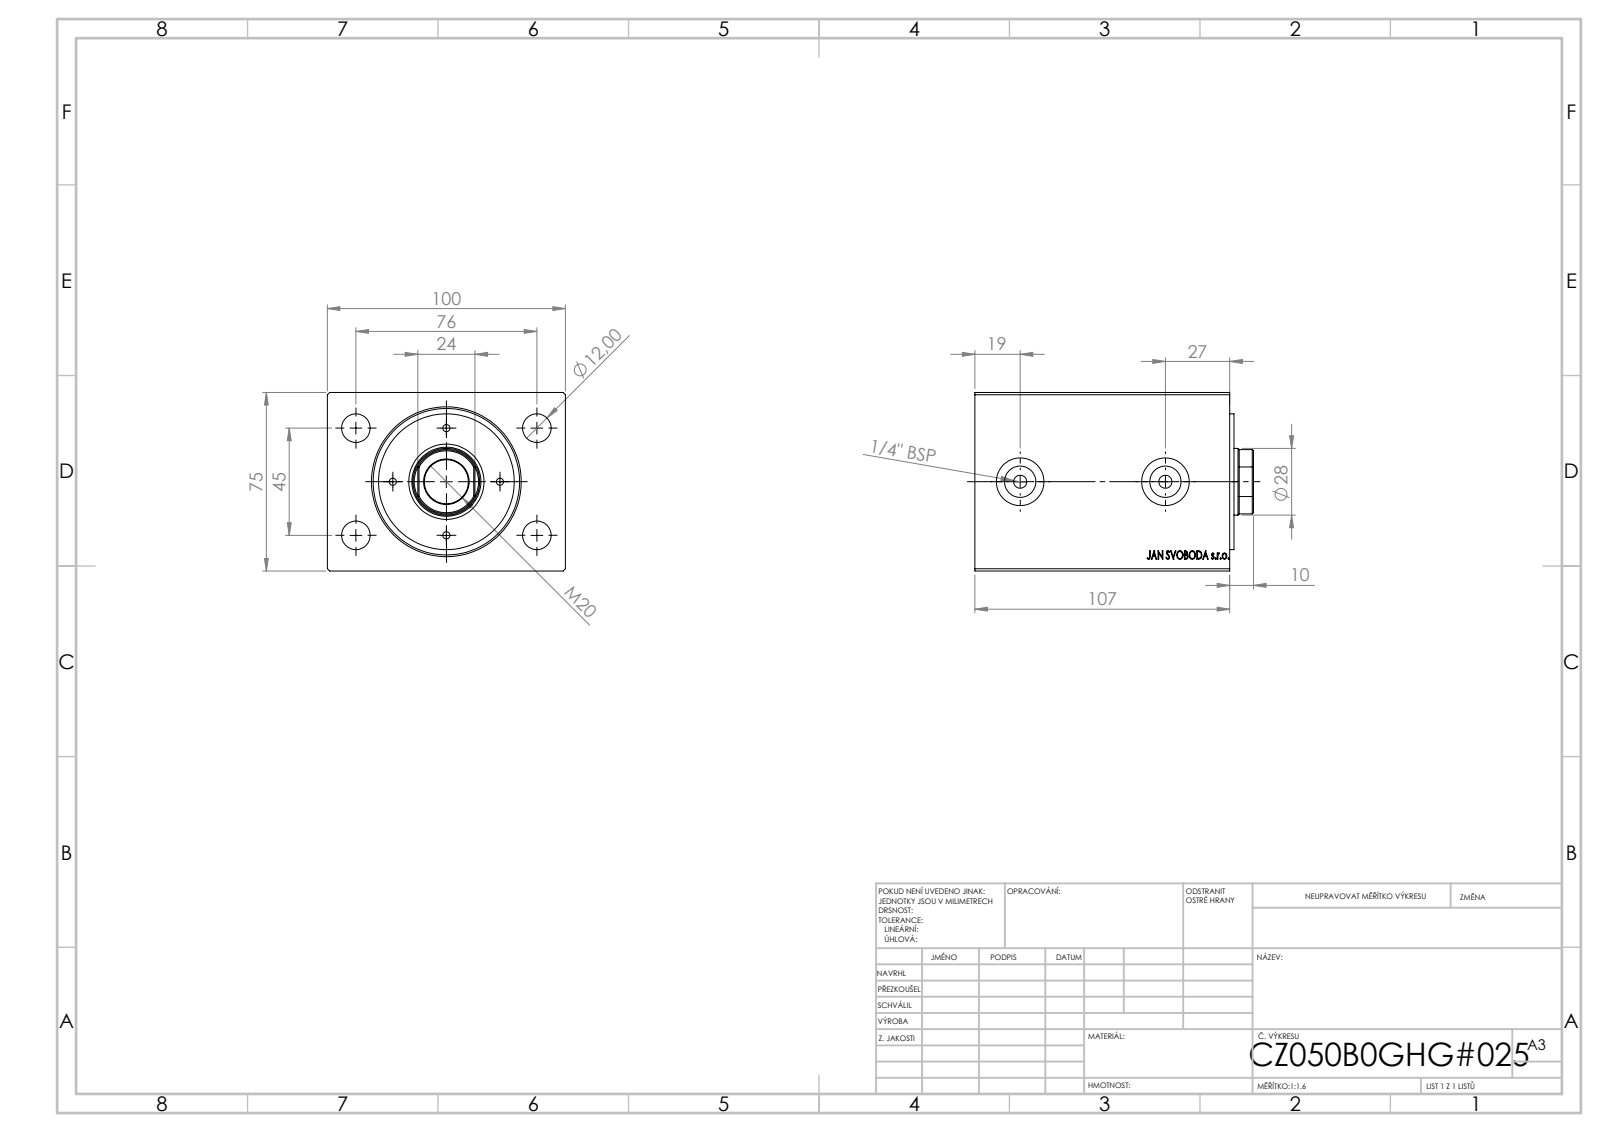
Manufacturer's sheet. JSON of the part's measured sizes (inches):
{"part_name": "V500CZ_B_VC; V500CZ", "step_written_by": "SolidWorks 2019 (CONFIG_CONTROL_DESIGN)", "units": "inches", "bodies": {"solids": 3, "faces": 873, "planar": 399, "cylindrical": 58, "other": 416}, "overall_size": [4.606, 3.937, 2.953], "volume_in3": 49.49, "surface_area_in2": 190.6, "round_holes": [[0.118, 4], [0.472, 4], [0.217, 2], [0.518, 2], [0.787, 2], [0.728, 1], [1.102, 1], [1.142, 1], [1.417, 1], [1.969, 1], [2.421, 1]], "round_bosses_or_shafts": [[2.244, 1]], "partial_cylinders_radius": [[0.531, 1]], "face_to_face_distances": [2.953, 3.937, 4.213, 3.524, 0.689, 3.228, 0.295, 0.984, 3.594, 0.071], "hole_center_spacings": [0.886, 1.076, 1.253, 1.496, 1.739, 1.772, 2.319, 2.541]}
